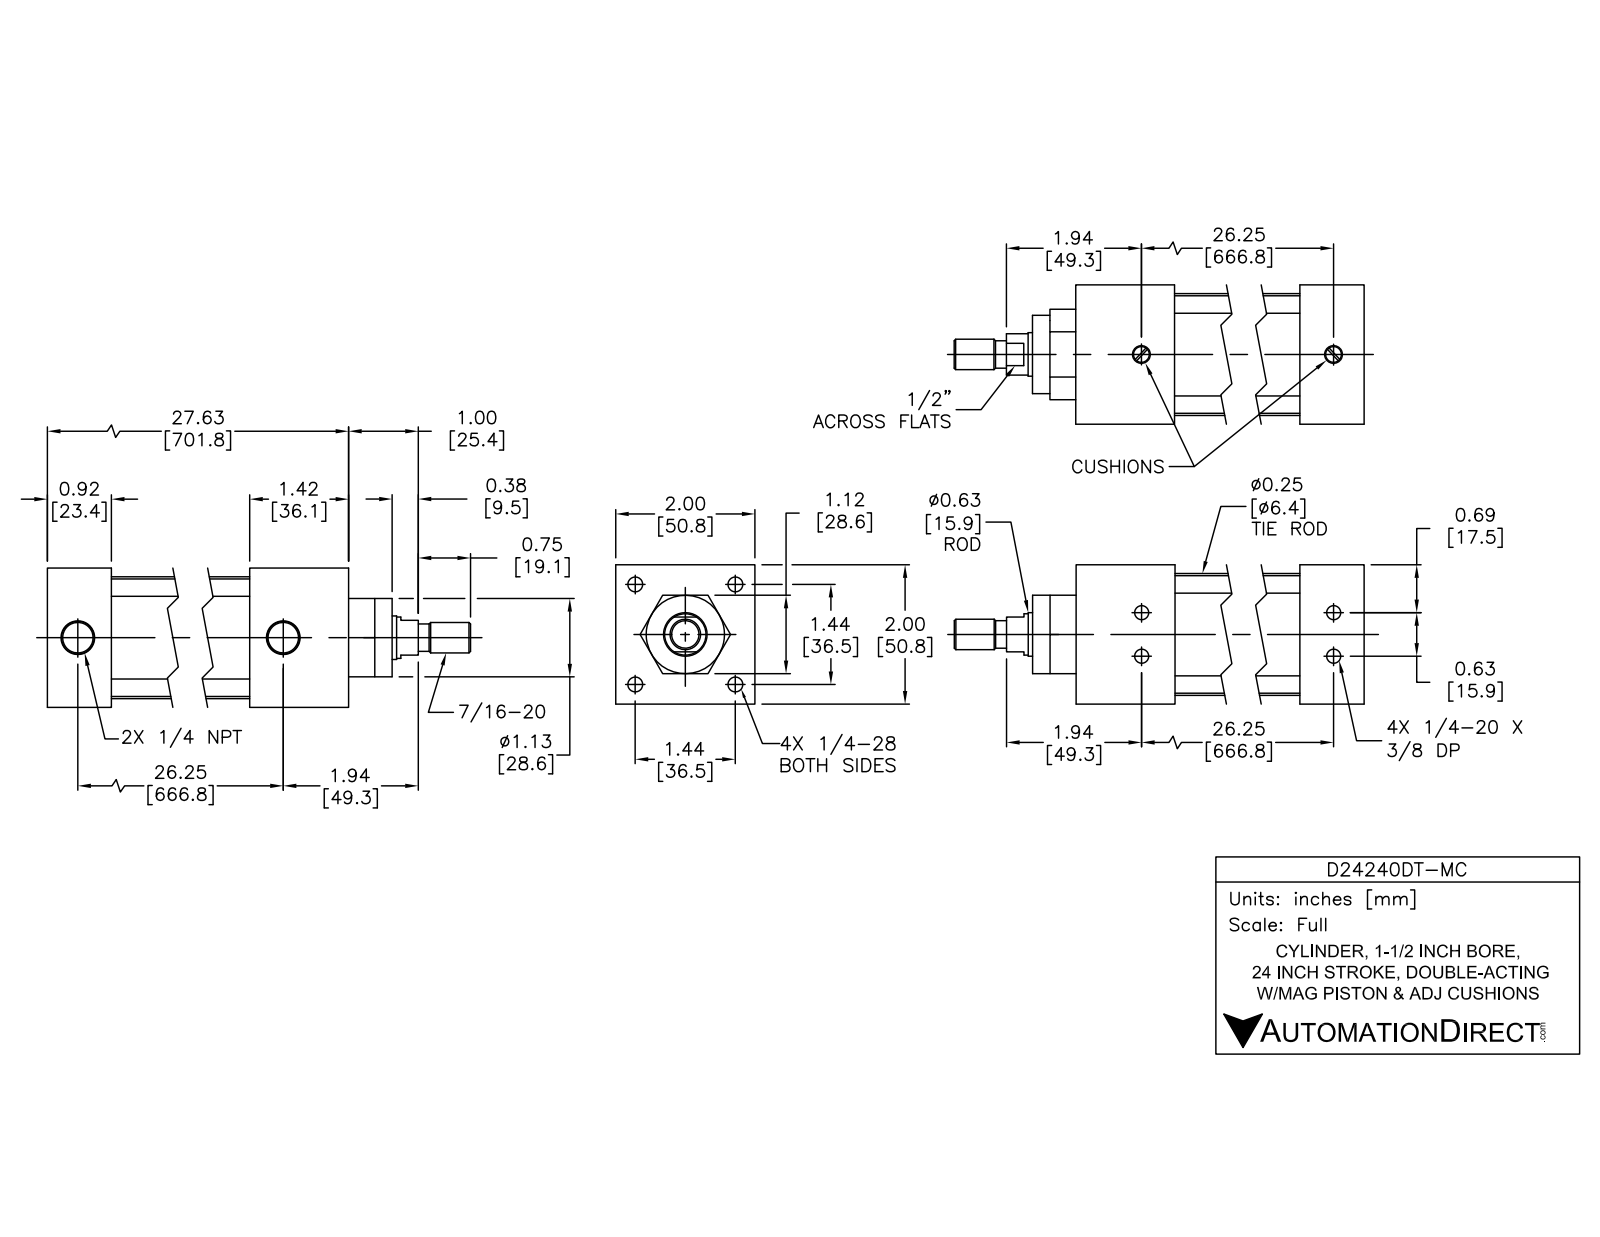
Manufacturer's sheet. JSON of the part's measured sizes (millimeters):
{"part_name": "D24240DT-M BODY; D24240DT-M PISTON; D24240DT-MC", "step_written_by": "SolidWorks 2015 (AUTOMOTIVE_DESIGN)", "units": "millimeters", "bodies": {"solids": 12, "faces": 303, "planar": 99, "cylindrical": 114, "other": 90}, "overall_size": [746, 50.8, 50.8], "volume_mm3": 639300, "surface_area_mm2": 291600, "round_holes": [[5, 4], [5.4, 4], [7.1, 4], [10.3, 4], [7.5, 2], [12.1, 2], [15.9, 1], [16, 1], [38.1, 1]], "round_bosses_or_shafts": [[9.9, 4], [6.4, 4], [5.6, 4], [44.5, 1], [38, 1], [28.5, 1], [15.8, 1], [15, 1]], "partial_cylinders_radius": [[5.1, 4]], "face_to_face_distances": [50.8, 2, 640.1, 701.6, 36.1, 665.5, 678.2, 642.1, 23.4, 28.5], "hole_center_spacings": [8, 666.7, 15.9, 25.8, 25.8, 36.4, 36.4, 51.5]}
